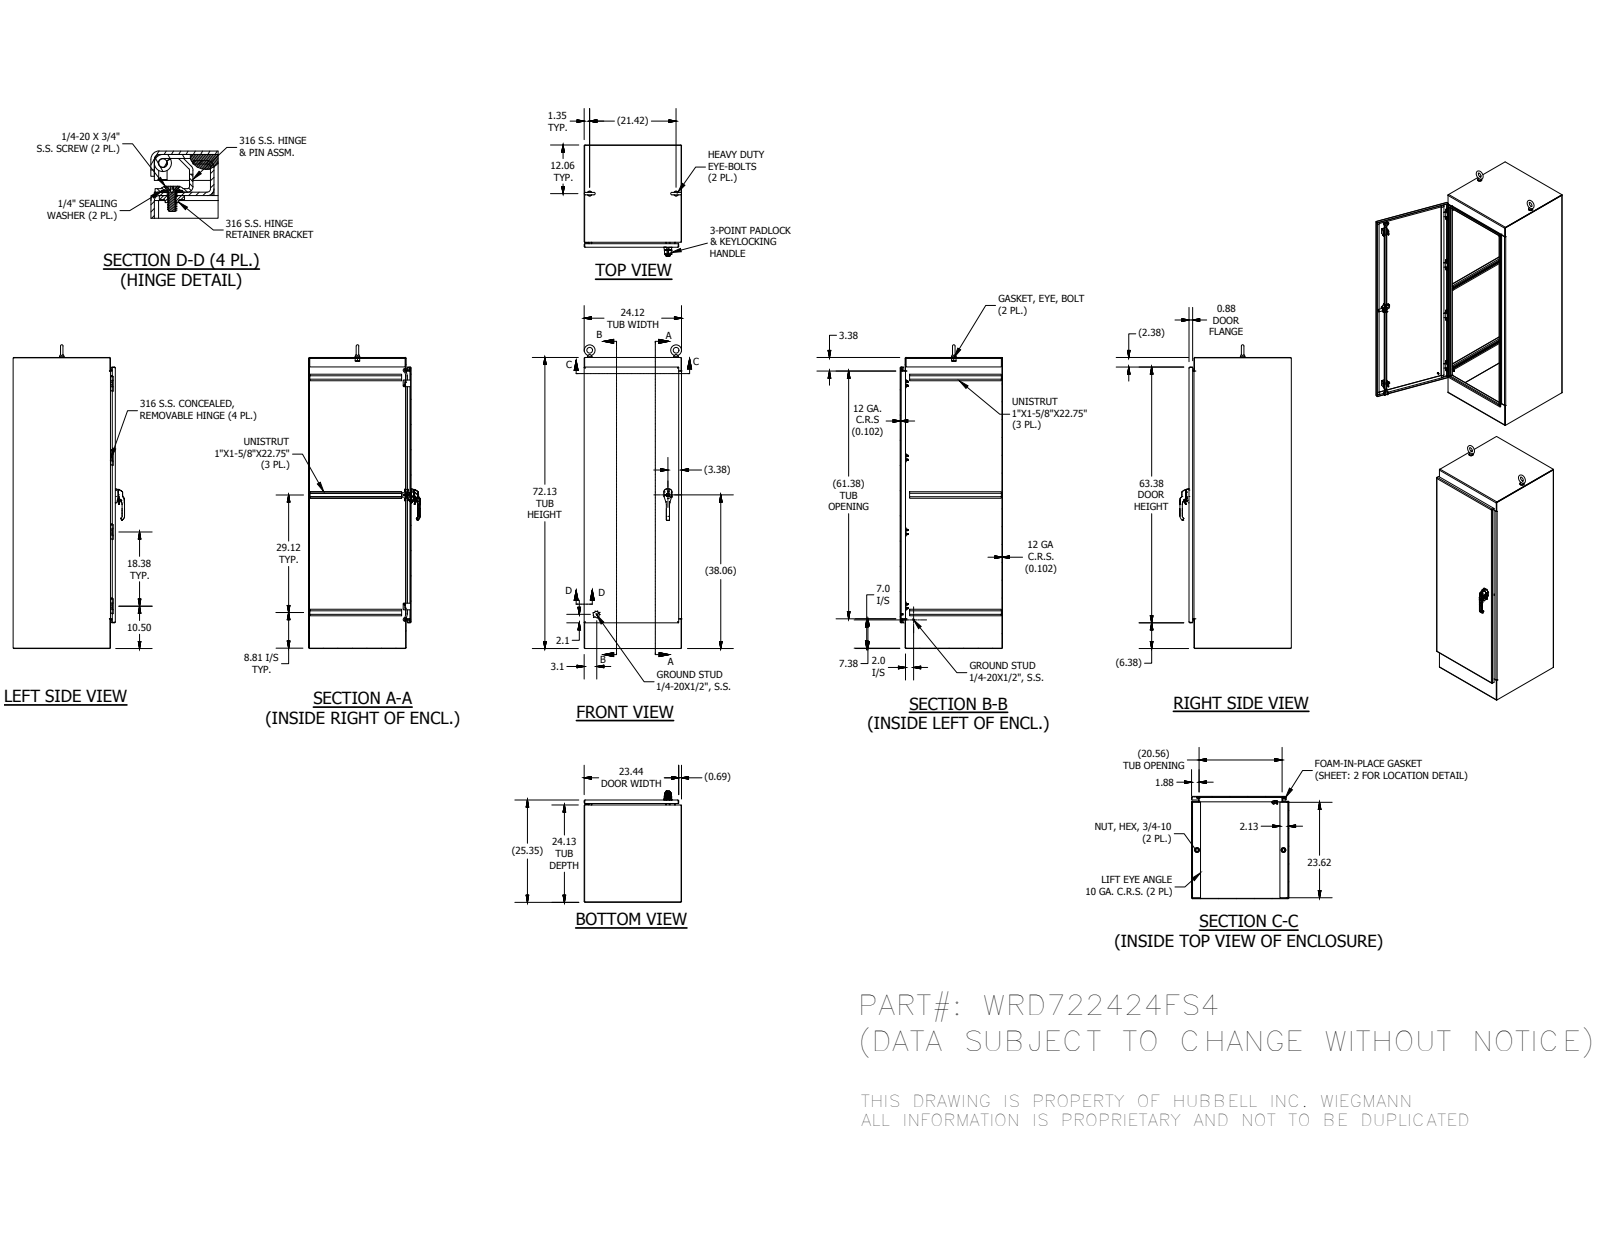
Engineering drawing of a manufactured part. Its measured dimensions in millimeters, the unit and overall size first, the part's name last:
Units: millimetres
Overall size (bounding box): 1911.29 × 701.44 × 612.83
Round holes (diameter × count): ⌀5.84 ×8, ⌀7.02 ×8, ⌀7.14 ×8, ⌀16.51 ×8, ⌀5.08 ×4, ⌀5.4 ×3, ⌀6 ×3, ⌀7.11 ×3, ⌀6.13 ×2, ⌀6.35 ×2, ⌀6.41 ×2, ⌀10.16 ×2
Round bosses / shafts (diameter × count): ⌀6.35 ×15, ⌀15.88 ×8, ⌀10.25 ×8, ⌀4.63 ×8, ⌀31.75 ×2, ⌀28.45 ×2, ⌀25.4 ×2, ⌀19.05 ×2
Partial cylindrical surfaces — rounded edges, fillets, slot ends (radius × count): R0.5 ×165, R0.3 ×84, R1.59 ×27, R0.25 ×24, R3.17 ×20, R0.47 ×19, R2 ×15, R1.27 ×14
Main face-to-face distances: 2.59, 610.19, 641.23, 607.6, 612.78, 638.64, 643.82, 1829.39, 31.04, 1826.8
Hole centre spacings: 12.5, 25.4, 466.73, 933.45, 6.5, 22.5, 51.5, 6
Volume: 17 090 000 mm³ · Surface area: 12 860 000 mm²
Bodies: 85 solids, 3586 faces (1457 planar, 1207 cylindrical, 922 other)
Part name (STEP PRODUCT): WRD722424FS4BLR; WRD2424FS4TOP; WRD2424FS4BTM; WRD7224FS4DR (+8 more)
STEP written by: Autodesk Inventor 2016 (AUTOMOTIVE_DESIGN)
